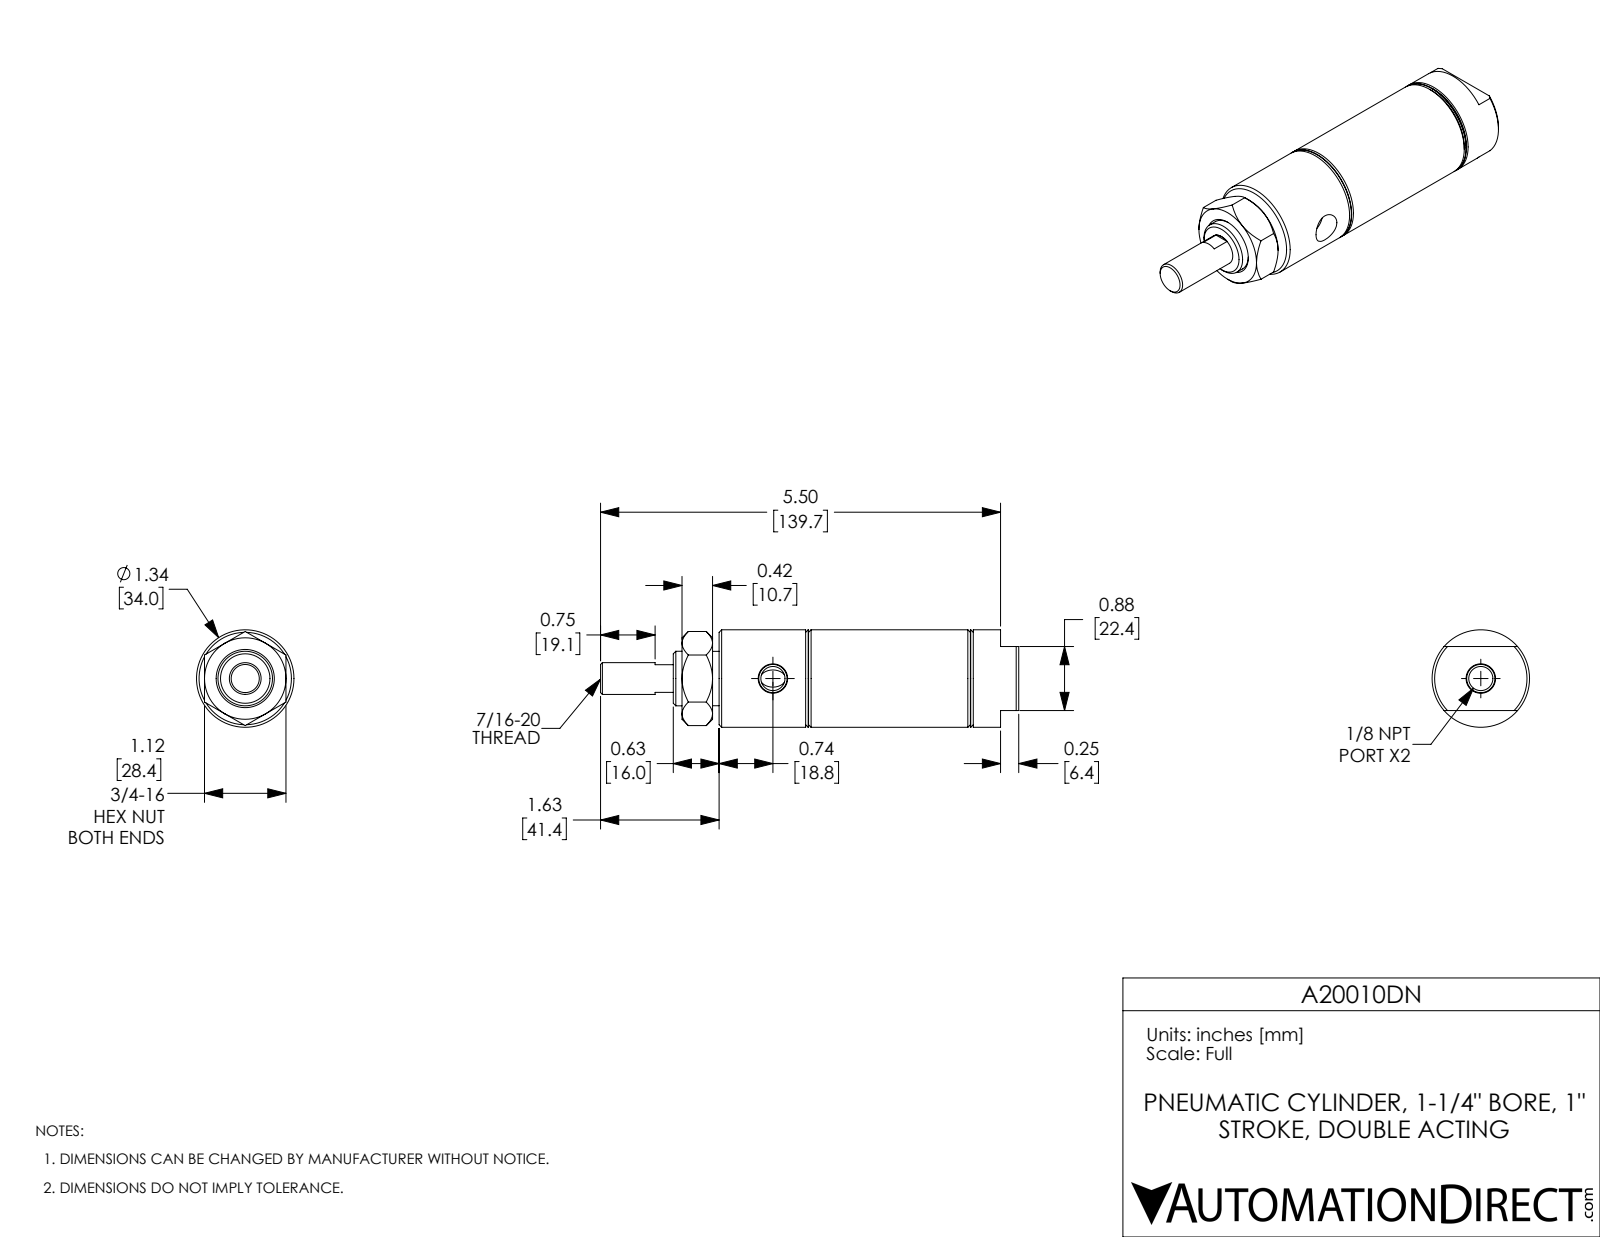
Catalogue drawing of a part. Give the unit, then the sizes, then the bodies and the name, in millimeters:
Units: millimetres
Overall size (bounding box): 146.1 × 34 × 34
Round holes (diameter × count): ⌀8.4 ×2, ⌀11.1 ×1, ⌀19.1 ×1, ⌀31.8 ×1
Round bosses / shafts (diameter × count): ⌀34 ×1, ⌀19 ×1
Main face-to-face distances: 25.4, 38.1, 12.7, 33.3, 46, 71.4, 104.6, 71.4, 58.7, 33.3
Volume: 84 410 mm³ · Surface area: 31 000 mm²
Bodies: 3 solids, 104 faces (33 planar, 30 cylindrical, 41 other)
Part name (STEP PRODUCT): A20010DN-Rod; A20010DN-MainBody; A20010DN; A20010DN_Mounting Nut_D-3556
STEP written by: SolidWorks 2017 (AUTOMOTIVE_DESIGN)
